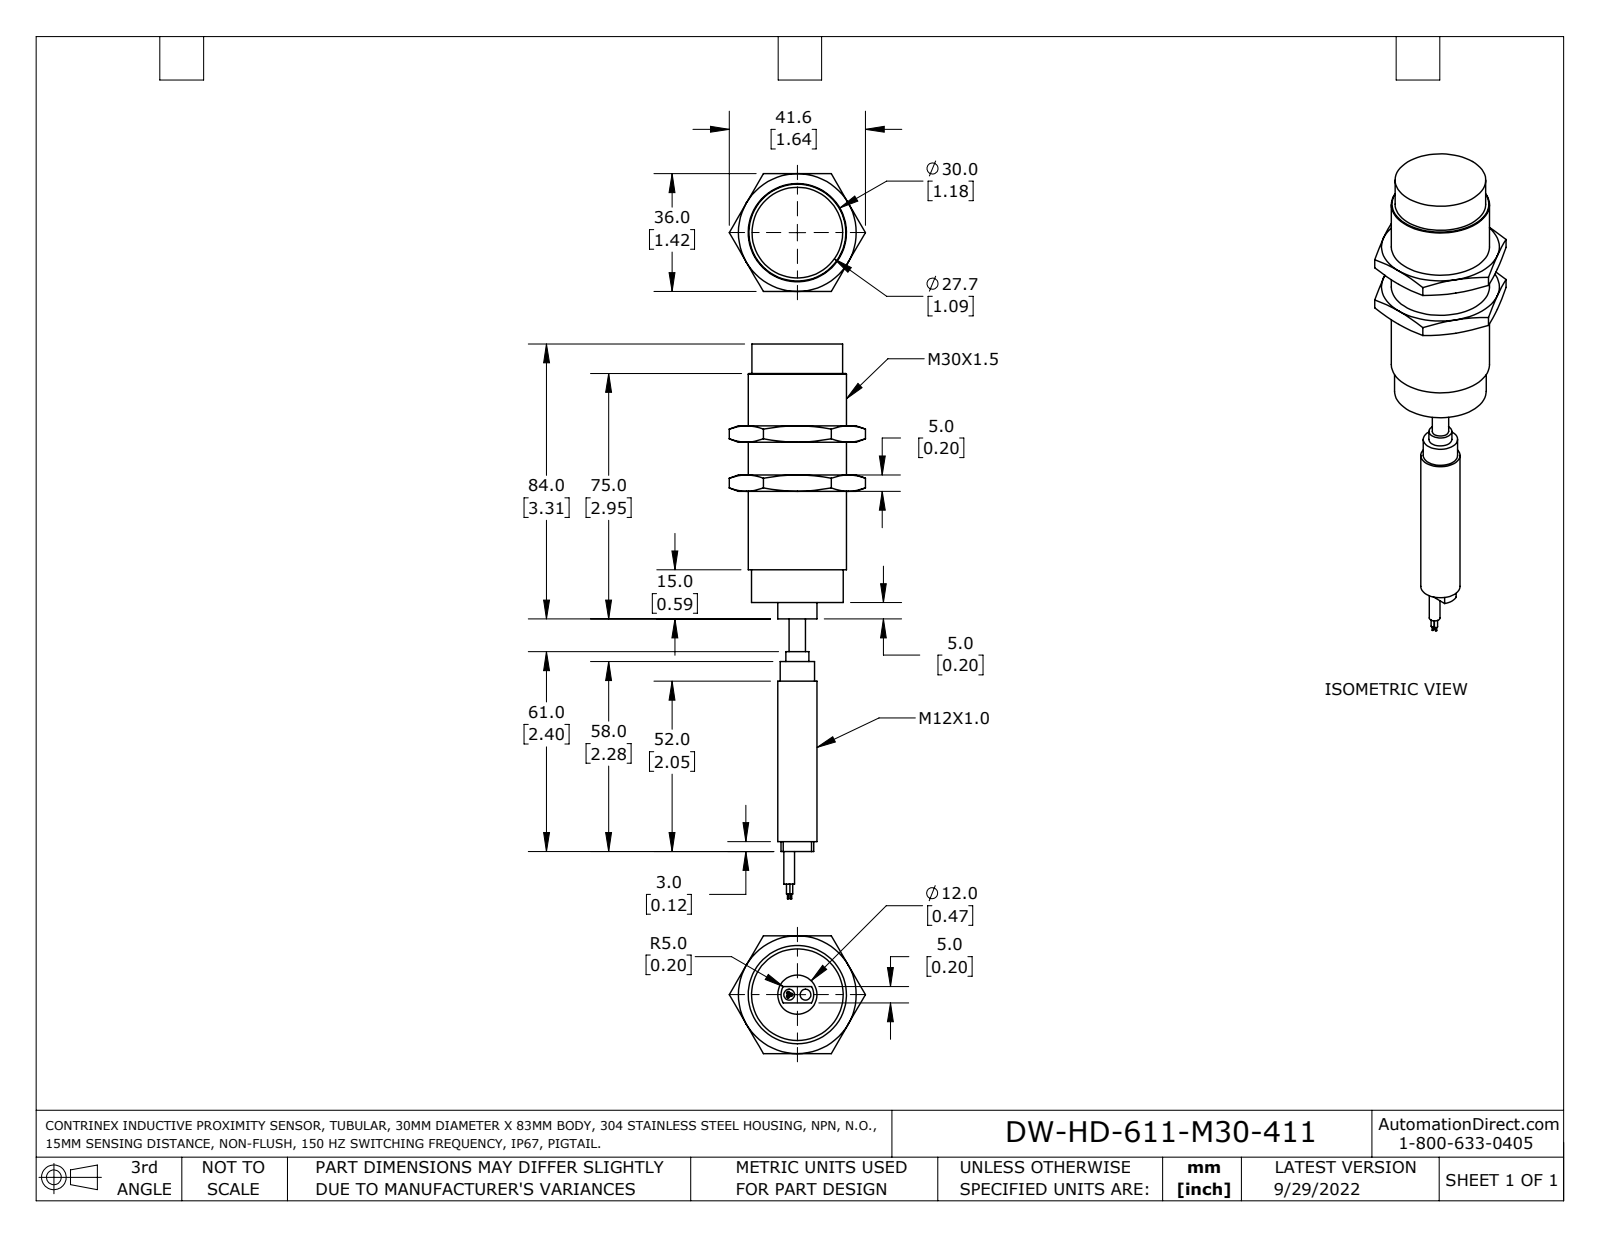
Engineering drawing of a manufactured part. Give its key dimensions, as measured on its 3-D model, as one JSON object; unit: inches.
{"part_name": "DW-HD-611-M30-411", "step_written_by": "SolidWorks 2021 (AUTOMOTIVE_DESIGN)", "units": "inches", "bodies": {"solids": 1, "faces": 81, "planar": 36, "cylindrical": 20, "other": 25}, "overall_size": [6.673, 1.637, 1.417], "volume_in3": 3.977, "surface_area_in2": 20.83, "round_holes": [[0.13, 1]], "round_bosses_or_shafts": [[0.039, 3], [0.016, 3], [1.181, 1], [1.102, 1], [1.091, 1], [0.472, 1], [0.413, 1], [0.276, 1]], "partial_cylinders_radius": [[0.197, 1]], "face_to_face_distances": [0.197, 0.591, 1.417, 3.11, 1.535, 0.394, 2.126, 1.929, 1.339, 0.984]}
